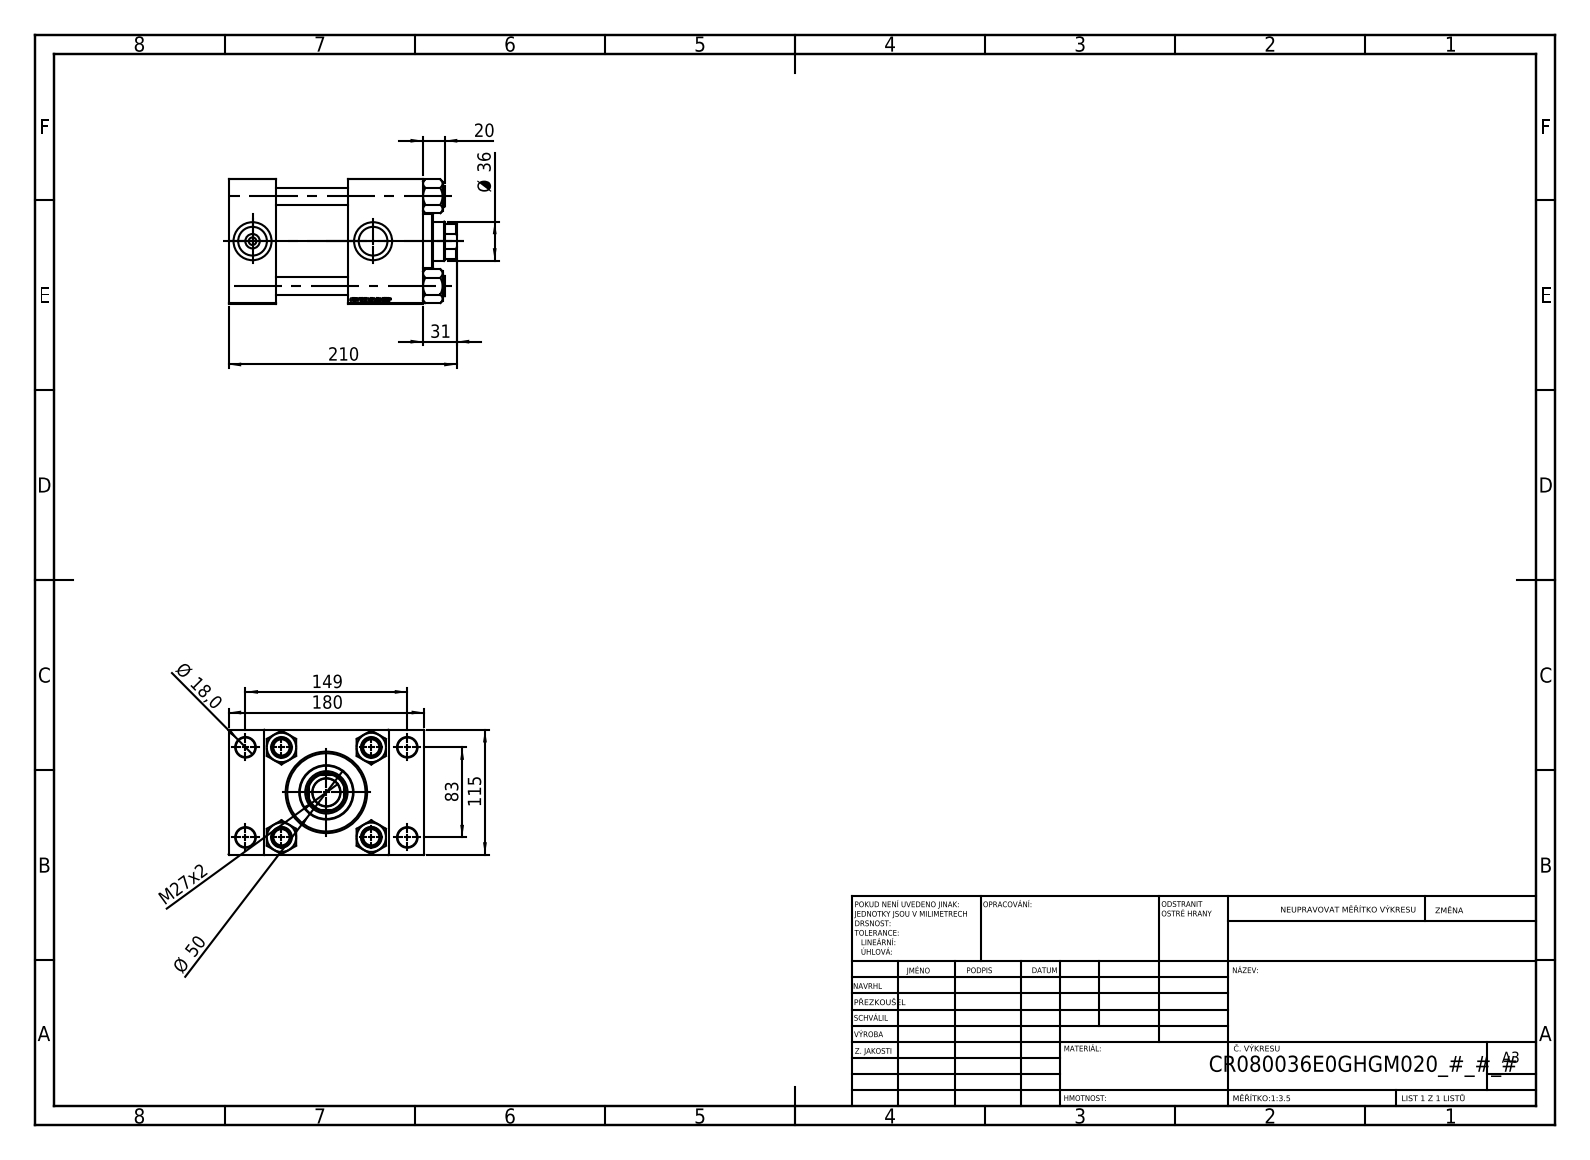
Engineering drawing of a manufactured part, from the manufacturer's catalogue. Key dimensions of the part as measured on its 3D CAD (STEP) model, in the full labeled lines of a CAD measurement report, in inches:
Part name (STEP PRODUCT): V215_VC_A; NUT_M5_E; V215CR_TYCINKA_E; V215CR_E_Body (+1 more)
STEP written by: SolidWorks 2019 (CONFIG_CONTROL_DESIGN)
Units: inches
Bodies: 11 solids, 1184 faces (546 planar, 86 cylindrical, 552 other)
Overall size (bounding box): 8.268 × 7.087 × 4.528
Volume: 127.2 in³ · Surface area: 480.9 in²
Round holes (diameter × count): ⌀0.63 ×4, ⌀0.709 ×4, ⌀0.276 ×2, ⌀1.041 ×2, ⌀1.378 ×2, ⌀1.004 ×1, ⌀1.417 ×1, ⌀1.535 ×1, ⌀2.402 ×1, ⌀2.835 ×1, ⌀3.15 ×1
Round bosses / shafts (diameter × count): ⌀0.748 ×4, ⌀3.386 ×1, ⌀1.969 ×1
Partial cylindrical surfaces — rounded edges, fillets, slot ends (radius × count): R0.689 ×1
Main face-to-face distances: 4.528, 1.732, 7.047, 5.315, 1.28, 5.807, 4.331, 2.598, 2.717, 0.787
Hole centre spacings: 1.305, 2.302, 3.256, 3.357, 3.513, 4.561, 5.607, 3.268
